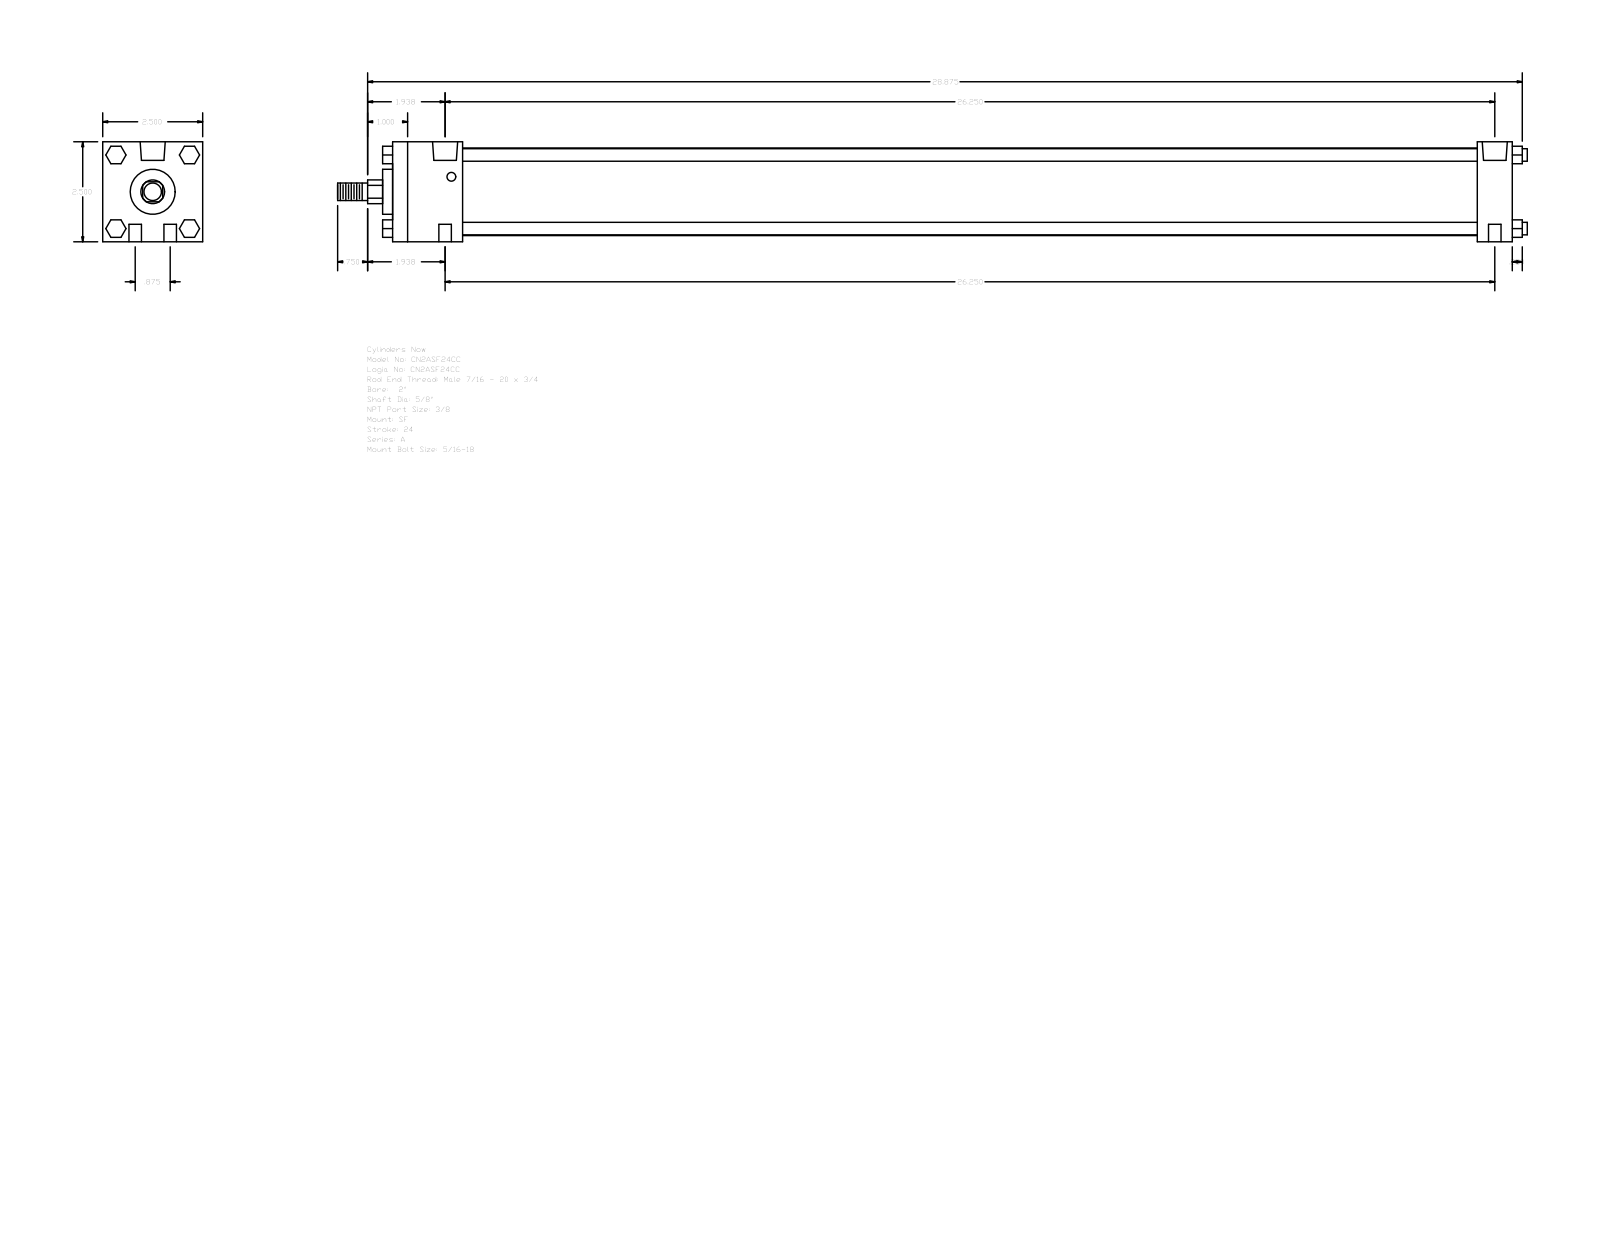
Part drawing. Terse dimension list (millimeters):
name: A_SF__0200_0.625
written by: GSSL Pune (CONFIG_CONTROL_DESIGN)
unit: mm
bodies: 0 solids, 124 faces (94 planar, 30 cylindrical, 0 other)
size: 755.65 × 63.5 × 63.5
holes: 4× ⌀7.94, 2× ⌀5.56, 2× ⌀15.93
bosses: 4× ⌀7.94, 1× ⌀55.63, 1× ⌀28.57, 1× ⌀15.88, 1× ⌀11.11
rounds: 1× R7.54
face distances: 63.5, 711.2, 688.97, 22.23, 44.45, 644.52, 666.75, 50.8, 6.35, 695.32
hole spacings: 11.11, 666.84, 666.75, 22.22, 667.12, 658.8
